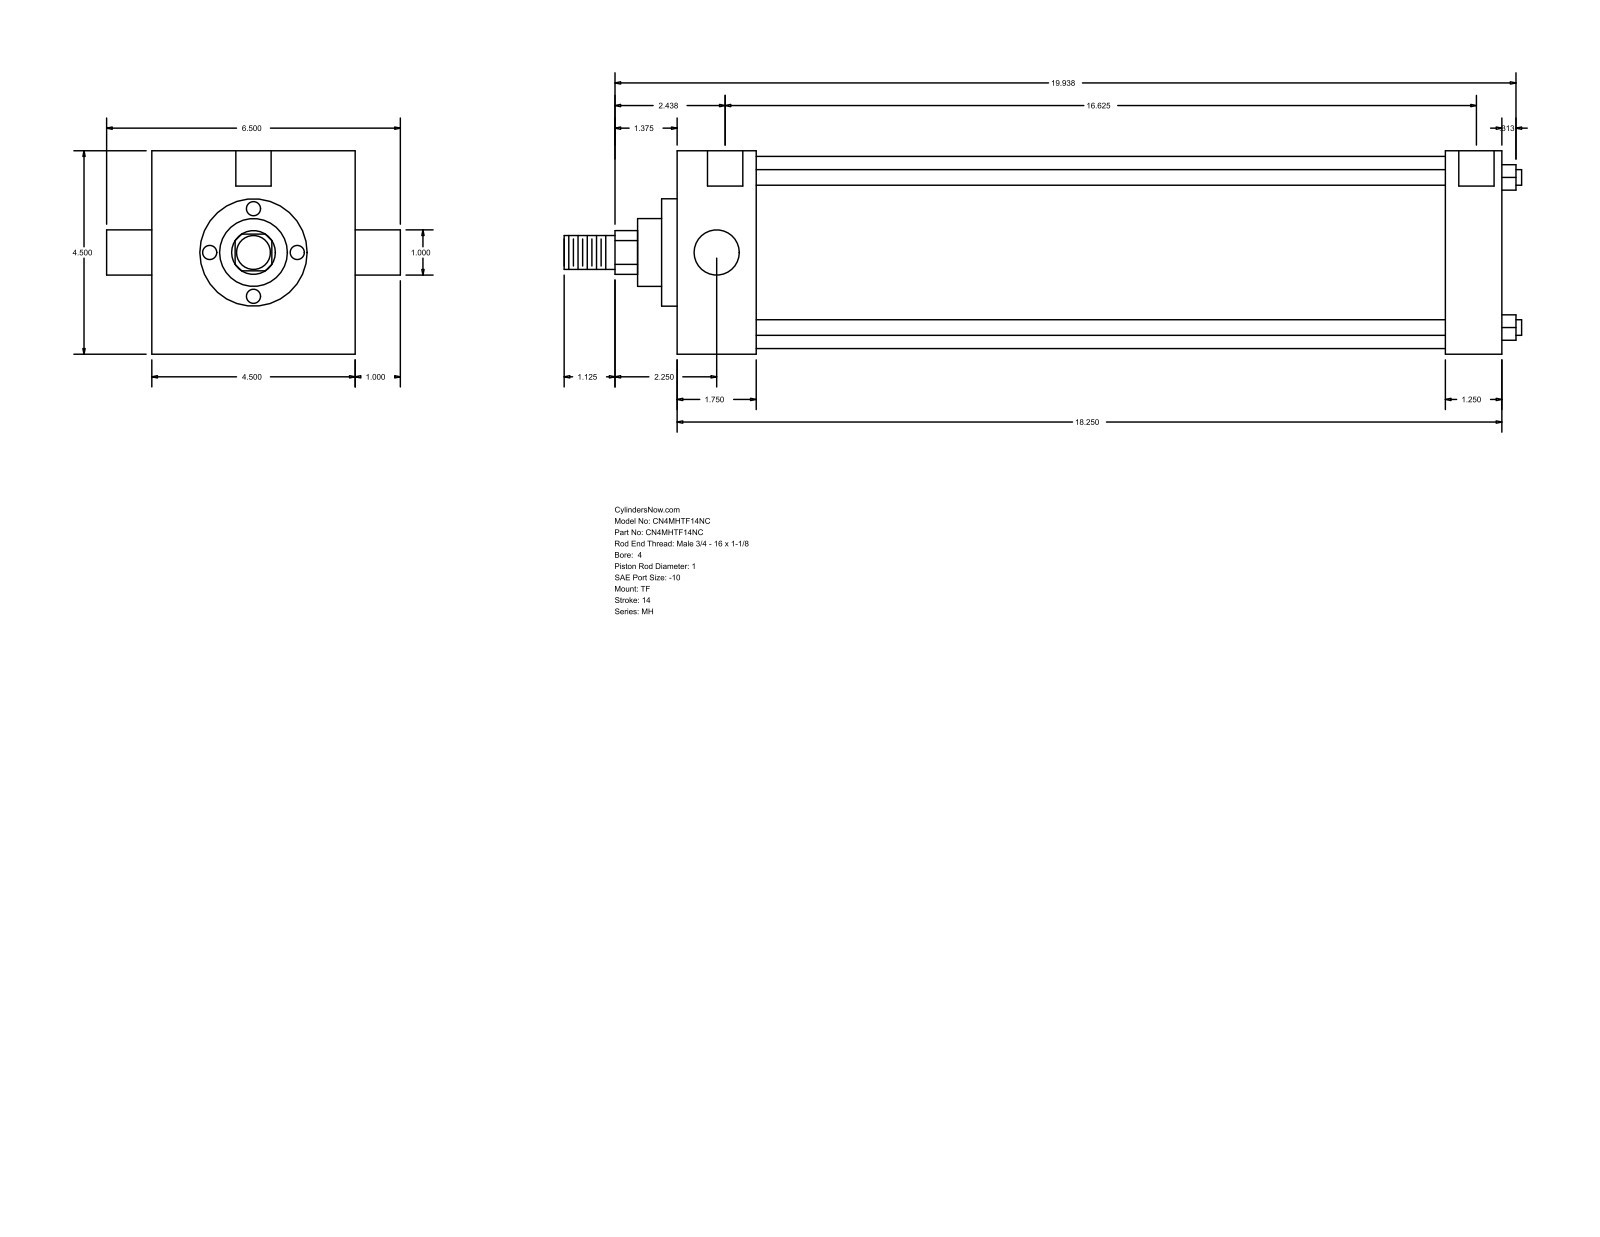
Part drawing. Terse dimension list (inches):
name: MH_TF__0400_1
written by: GSSL Pune (CONFIG_CONTROL_DESIGN)
unit: in
bodies: 0 solids, 86 faces (61 planar, 25 cylindrical, 0 other)
size: 21.187 × 6.5 × 4.5
holes: 3× ⌀0.344, 2× ⌀0.781
bosses: 4× ⌀0.345, 2× ⌀1, 1× ⌀4.25, 1× ⌀2.375, 1× ⌀1.5, 1× ⌀0.75
rounds: 1× R0.484
face distances: 4.5, 18.25, 1.75, 16.5, 17, 15.25, 1.25, 0.344, 2.094, 17.344
hole spacings: 0.062, 16.687, 16.625, 16.75
